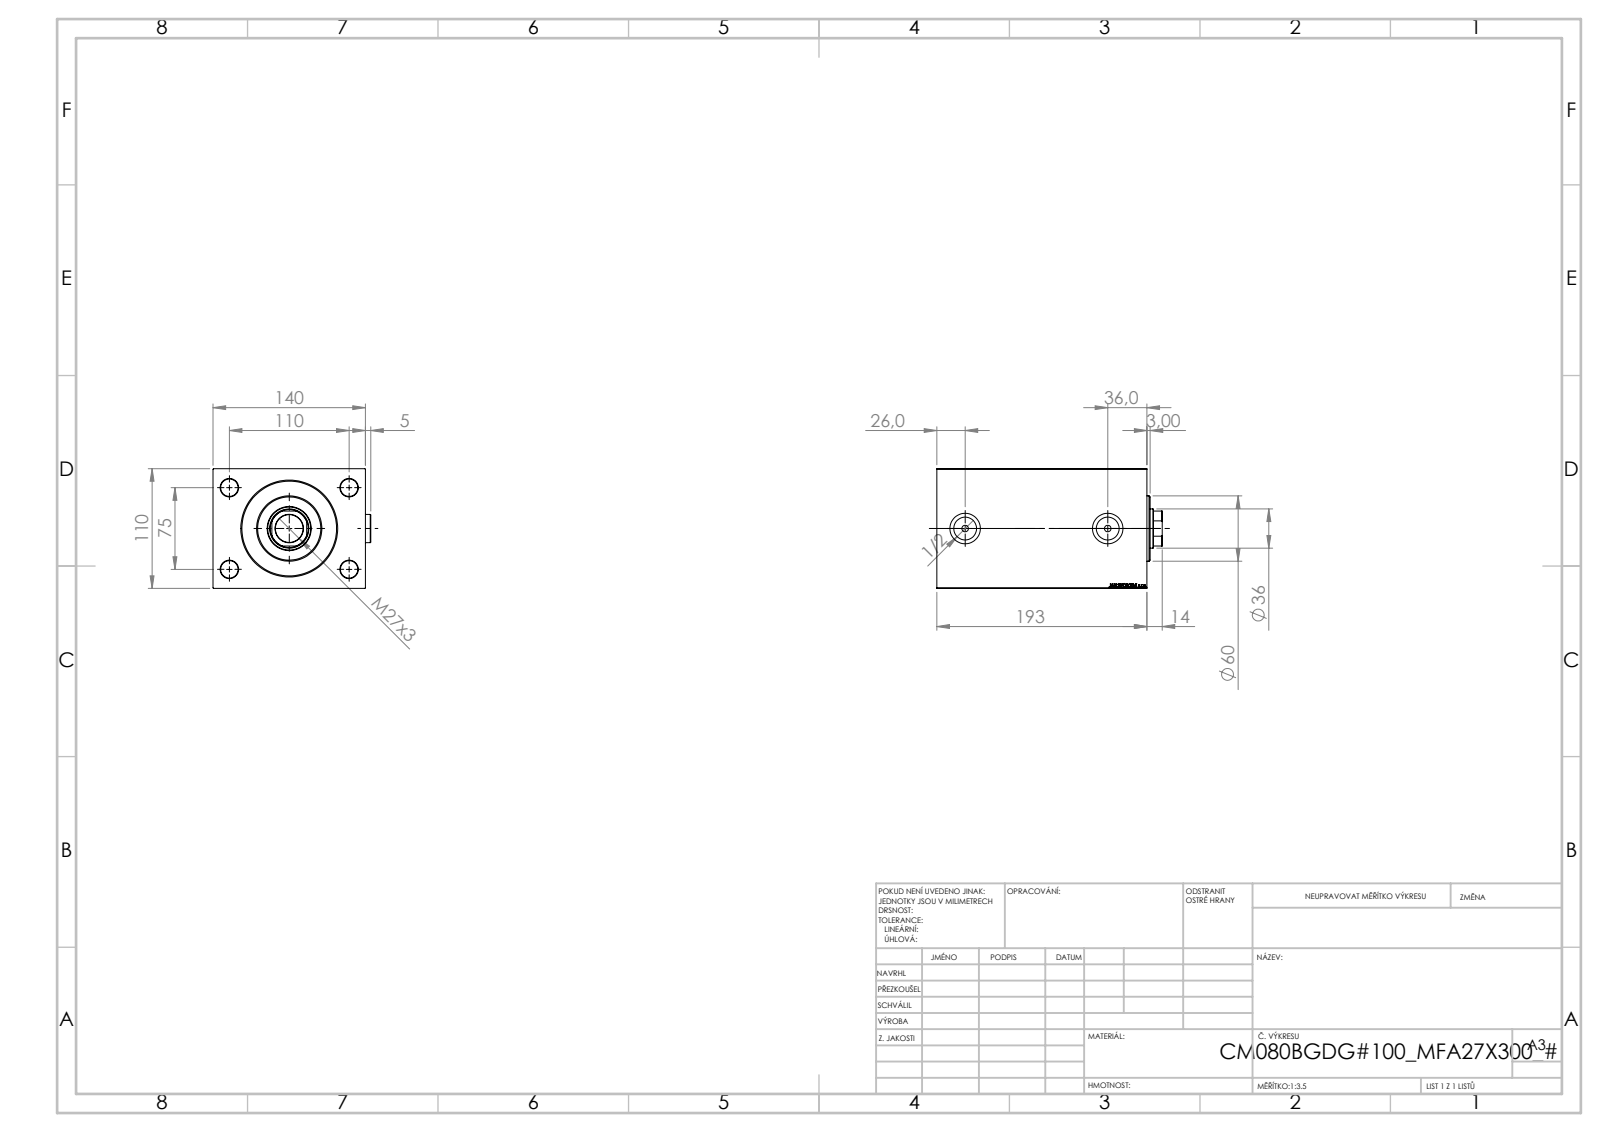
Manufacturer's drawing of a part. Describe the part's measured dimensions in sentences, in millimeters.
The part is named "Zatka_OIL_PORT; V450CM_B_VCP; V450CM_B_Body; V450CM_VC_B". Its 3-D file was written by "SolidWorks 2019 (CONFIG_CONTROL_DESIGN)". It is 5 solids with 938 faces: 436 planar, 72 cylindrical and 430 other. Overall it measures 207 by 144.9 by 110 millimeters. Its volume is 2 506 000 cubic millimeters and its surface area 247 842 square millimeters. Round holes: 4 of diameter 16, 2 of diameter 6, 2 of diameter 20.96, 2 of diameter 28, 1 of diameter 25.5, 1 of diameter 36, 1 of diameter 39.5, 1 of diameter 40.5, 1 of diameter 80, 1 of diameter 82, 1 of diameter 87. Round bosses or shafts: 2 of diameter 26, 1 of diameter 60. Partial cylindrical surfaces (rounded edges, fillets, slot ends): 1 of radius 17.5. The main face-to-face distances are 110, 140, 193, 172, 21, 14, 158, 179, 114, 100. The hole center spacings are 66.57, 75, 110, 133.14, 131.
